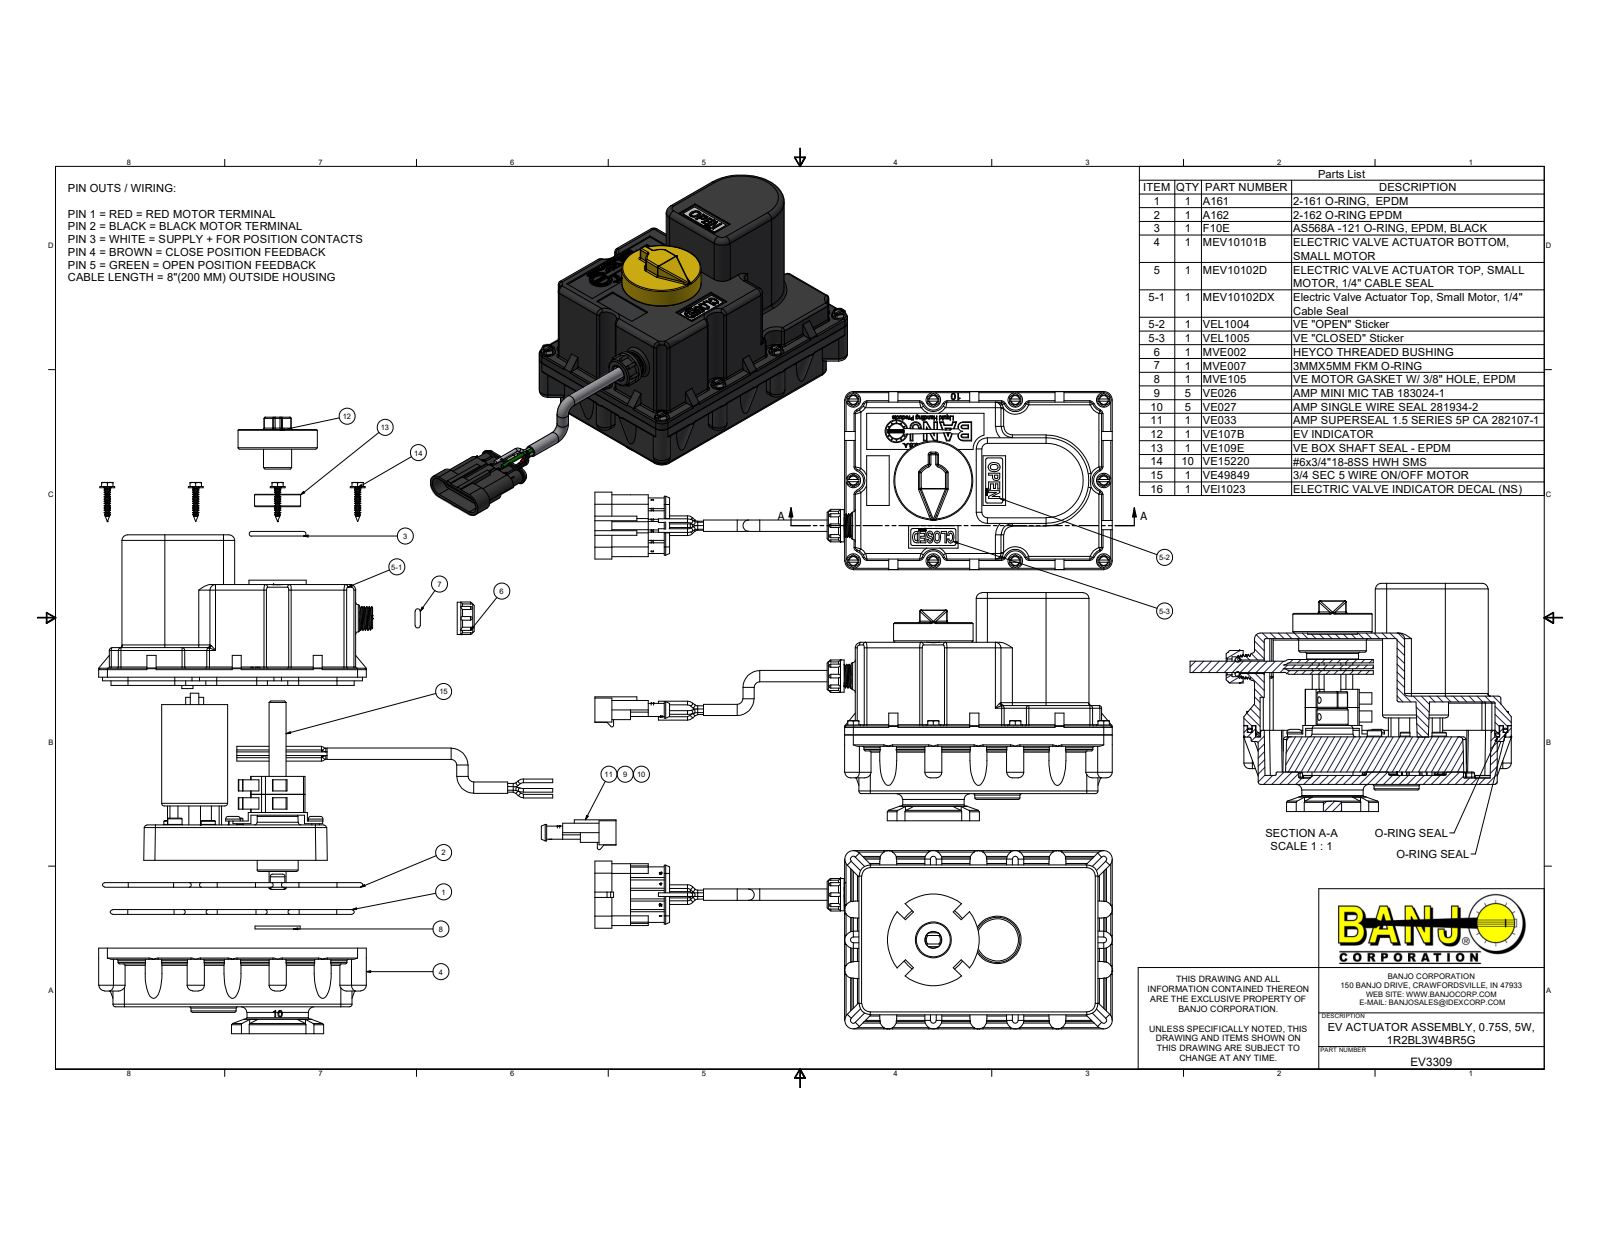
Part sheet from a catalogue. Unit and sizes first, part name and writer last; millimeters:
Units: millimetres
Overall size (bounding box): 291.2 × 128.4 × 100.3
Round holes (diameter × count): ⌀4.1 ×11, ⌀2.8 ×10, ⌀5.1 ×10, ⌀3 ×6, ⌀3.8 ×6, ⌀4.5 ×6, ⌀1.4 ×5, ⌀5.5 ×5, ⌀2.5 ×2, ⌀3.3 ×2, ⌀7.6 ×1, ⌀8.6 ×1
Round bosses / shafts (diameter × count): ⌀2 ×19, ⌀8.3 ×10, ⌀3.5 ×10, ⌀2.6 ×8, ⌀5.9 ×5, ⌀4.4 ×5, ⌀3.9 ×5, ⌀3.4 ×5
Partial cylindrical surfaces — rounded edges, fillets, slot ends (radius × count): R0.8 ×121, R0.5 ×63, R1.5 ×47, R3.2 ×24, R8 ×24, R12.7 ×24, R0.5 ×21, R0.2 ×20
Main face-to-face distances: 3.2, 85.2, 5.1, 27.9, 26, 82, 33, 1.9, 19.8, 20.1
Hole centre spacings: 42.7, 52.3, 42.8, 45.3, 60.4, 6, 12.5, 30.2
Volume: 561 900 mm³ · Surface area: 249 900 mm²
Bodies: 43 solids, 4905 faces (2138 planar, 1304 cylindrical, 1463 other)
Part name (STEP PRODUCT): EV3309; MEV10101B; MEV10102D; MEV10102DX (+8 more)
STEP written by: Autodesk Inventor 2022 (AUTOMOTIVE_DESIGN)
